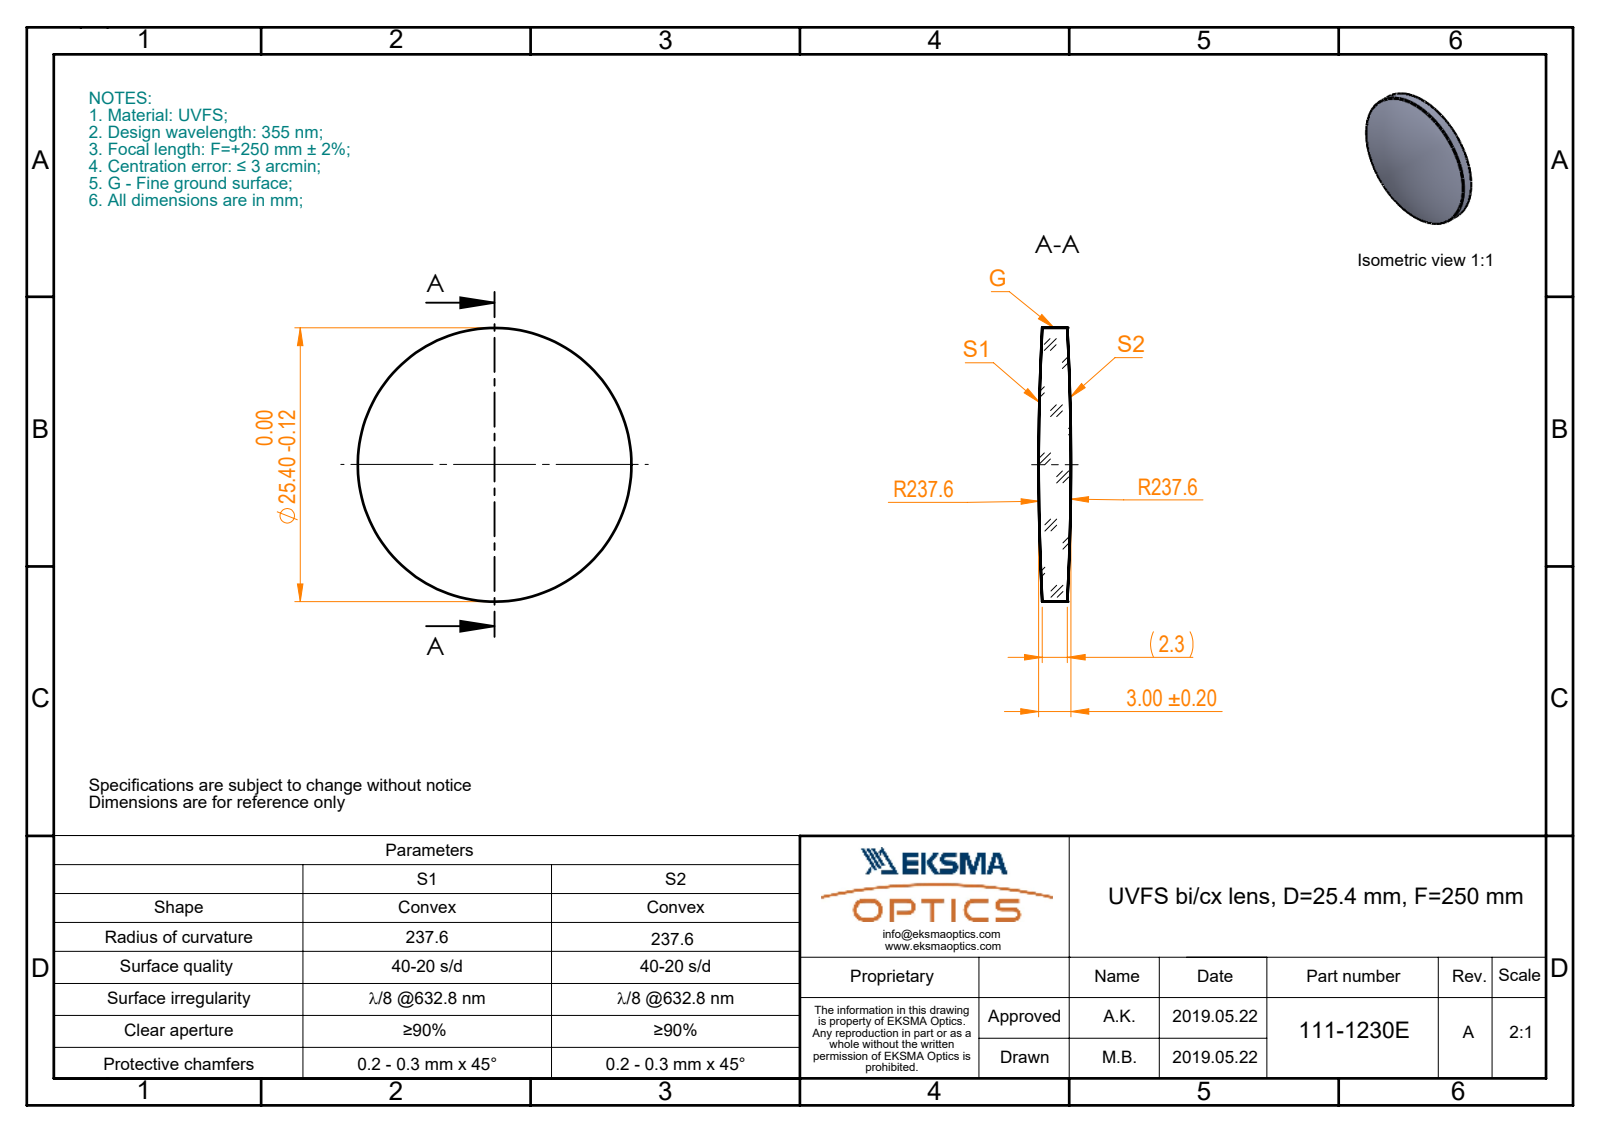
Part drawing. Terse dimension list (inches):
name: 111-1230E UVFS bi-cx 25.4 F250
written by: SolidWorks 2017 (CONFIG_CONTROL_DESIGN)
unit: in
bodies: 1 solid, 6 faces (0 planar, 2 cylindrical, 4 other)
size: 1 × 1 × 0.118
volume: 0.082 in³; area: 1.858 in²
bosses: 1× ⌀1
